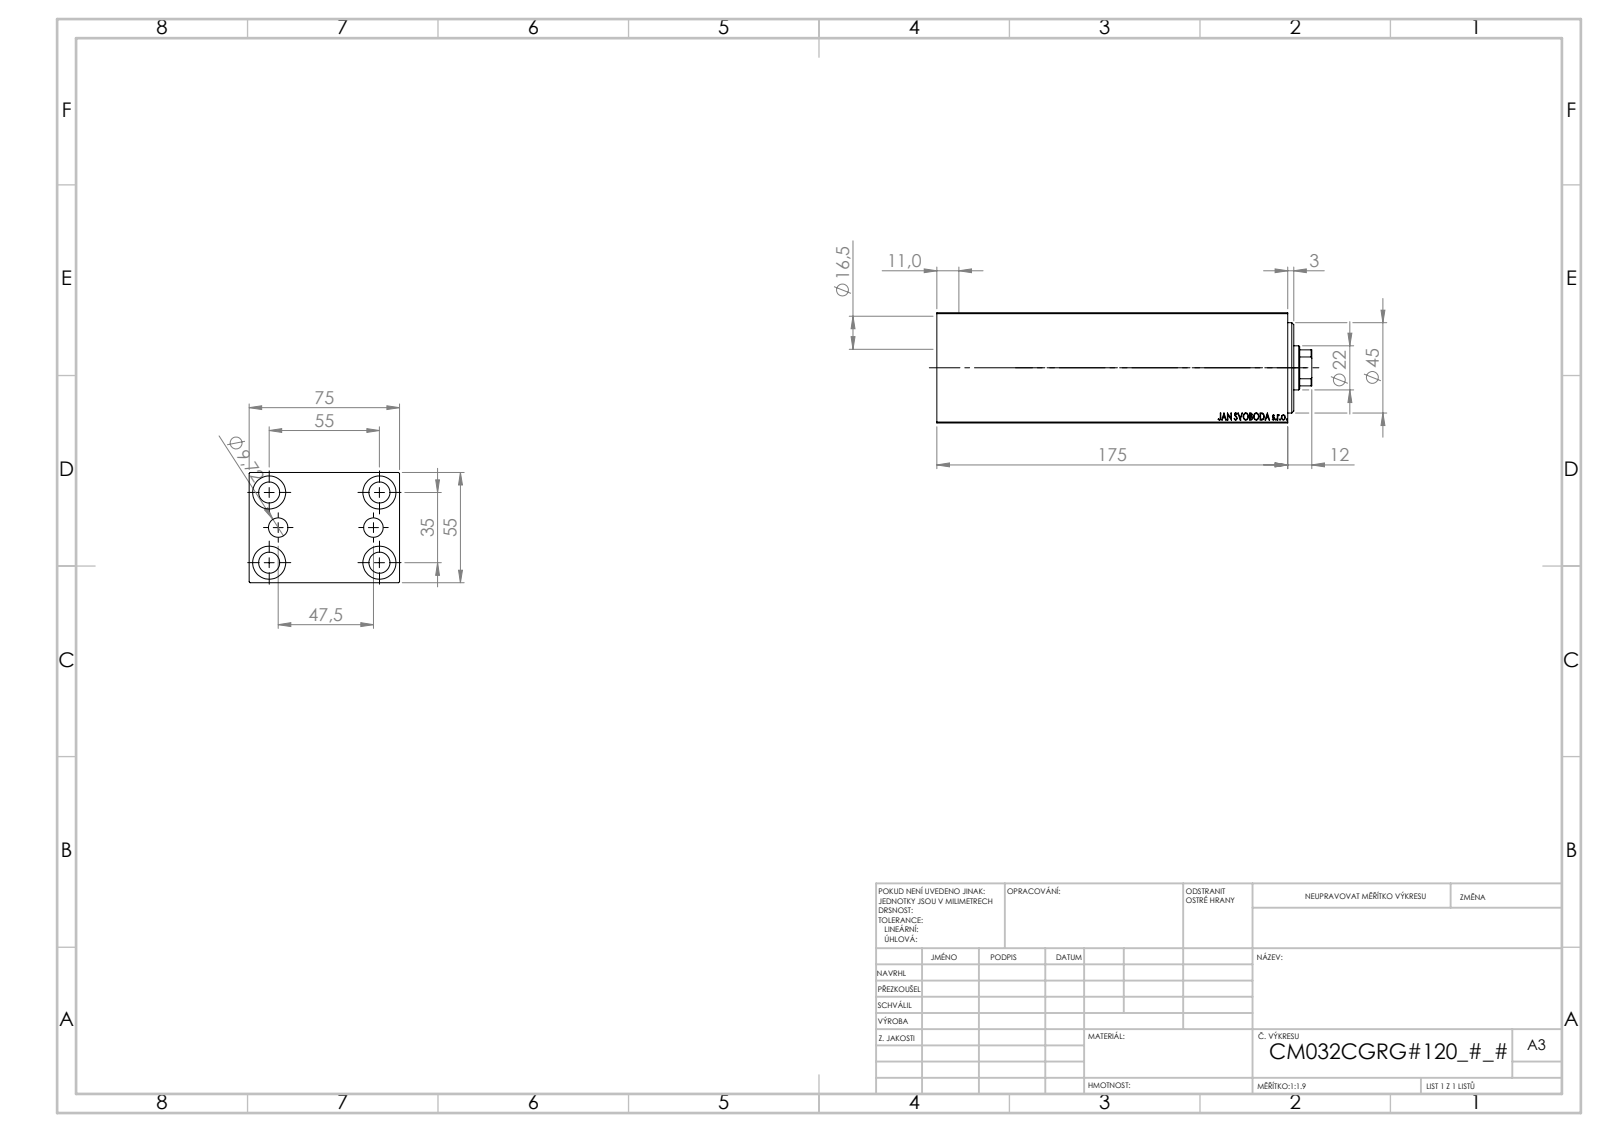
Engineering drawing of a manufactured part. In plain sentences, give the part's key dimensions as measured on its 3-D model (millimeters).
The part is named "V450CM_C_Body; V450CM_VC_B; V450CM_C_VCP". Its 3-D file was written by "SolidWorks 2019 (CONFIG_CONTROL_DESIGN)". It is 3 solids with 858 faces: 408 planar, 56 cylindrical and 394 other. Overall it measures 187 by 75 by 55 millimeters. Its volume is 599 372 cubic millimeters and its surface area 121 692 square millimeters. Round holes: 5 of diameter 10.5, 4 of diameter 16.5, 2 of diameter 4, 2 of diameter 9.72, 1 of diameter 22, 1 of diameter 25.5, 1 of diameter 32, 1 of diameter 34, 1 of diameter 45. Partial cylindrical surfaces (rounded edges, fillets, slot ends): 1 of radius 10.5. The main face-to-face distances are 55, 75, 10, 165, 175, 170, 5, 160, 11, 164. The hole center spacings are 17.9, 32.6, 54.16, 23.75, 35, 55, 65.19, 47.5.
